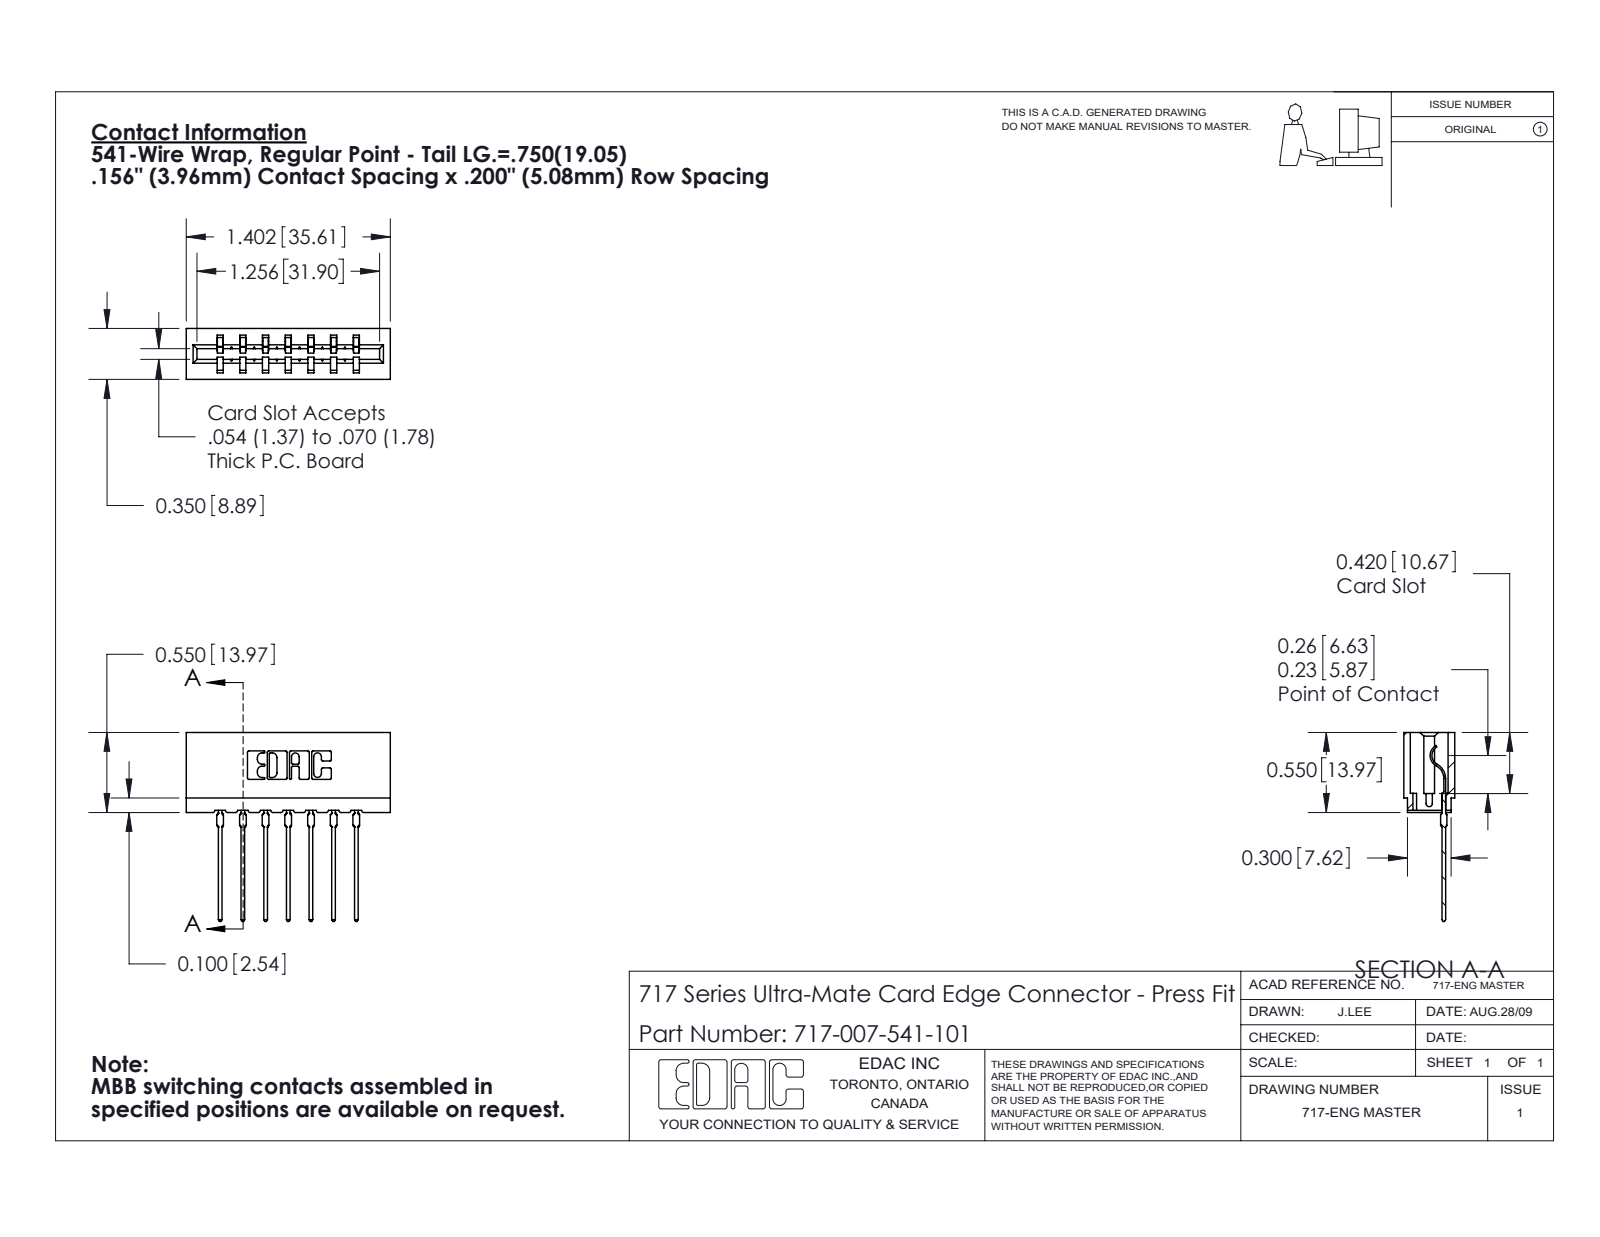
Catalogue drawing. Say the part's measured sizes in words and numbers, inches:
The part is named "745-292-001_541; 717-007-541-101; 717 Part_Insulator Option - 06". Its 3-D file was written by "SolidWorks 2020 (CONFIG_CONTROL_DESIGN)". It is 8 solids with 885 faces: 530 planar, 173 cylindrical and 182 other. Overall it measures 1.402 by 1.299 by 0.35 inches. Its volume is 0.195 cubic inches and its surface area 6.597 square inches. Partial cylindrical surfaces (rounded edges, fillets, slot ends): 22 of radius 0.01, 14 of radius 0.015, 14 of radius 0.021, 6 of radius 0.007, 6 of radius 0.031, 4 of radius 0.005, 4 of radius 0.011, 3 of radius 0.026. The main face-to-face distances are 0.212, 0.156, 0.138, 0.35, 0.198, 0.312, 0.468, 0.624, 0.042, 0.27.
